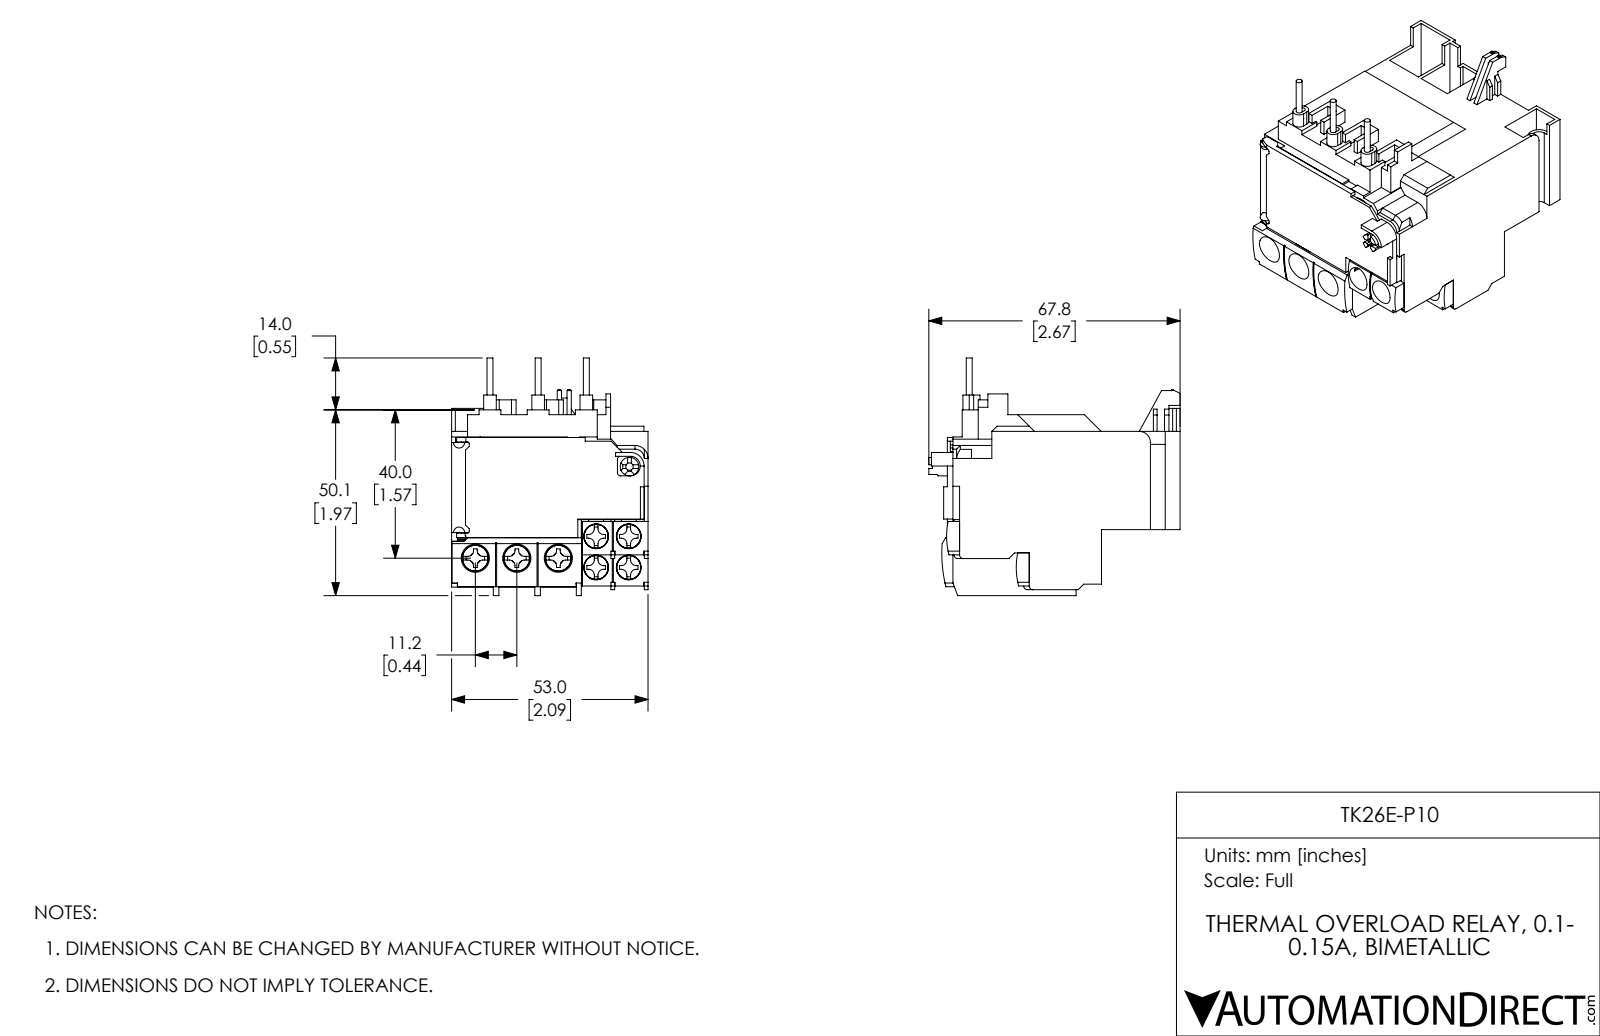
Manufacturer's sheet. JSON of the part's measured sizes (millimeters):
{"part_name": "TK26E-P10", "step_written_by": "SolidWorks 2017 (AUTOMOTIVE_DESIGN)", "units": "millimeters", "bodies": {"solids": 38, "faces": 1480, "planar": 1225, "cylindrical": 220, "other": 35}, "overall_size": [67.8, 64.1, 53], "volume_mm3": 99940, "surface_area_mm2": 38810, "round_holes": [[3.5, 4], [3.6, 4], [6.7, 4], [4, 3], [4.1, 3], [7.6, 3], [1, 1], [2, 1], [5, 1], [11, 1]], "round_bosses_or_shafts": [[6.6, 4], [1.6, 3], [6, 1]], "partial_cylinders_radius": [[1.5, 28], [1, 8], [0.5, 6], [1.7, 6], [0.8, 5], [1.2, 4], [4.3, 4], [4.8, 3]], "face_to_face_distances": [1, 9, 1.5, 12, 53, 2, 10, 11, 8.7, 0.7], "hole_center_spacings": [8.4, 8.8, 11.2, 12.2, 9.6, 10.5, 11.8, 18.8]}
